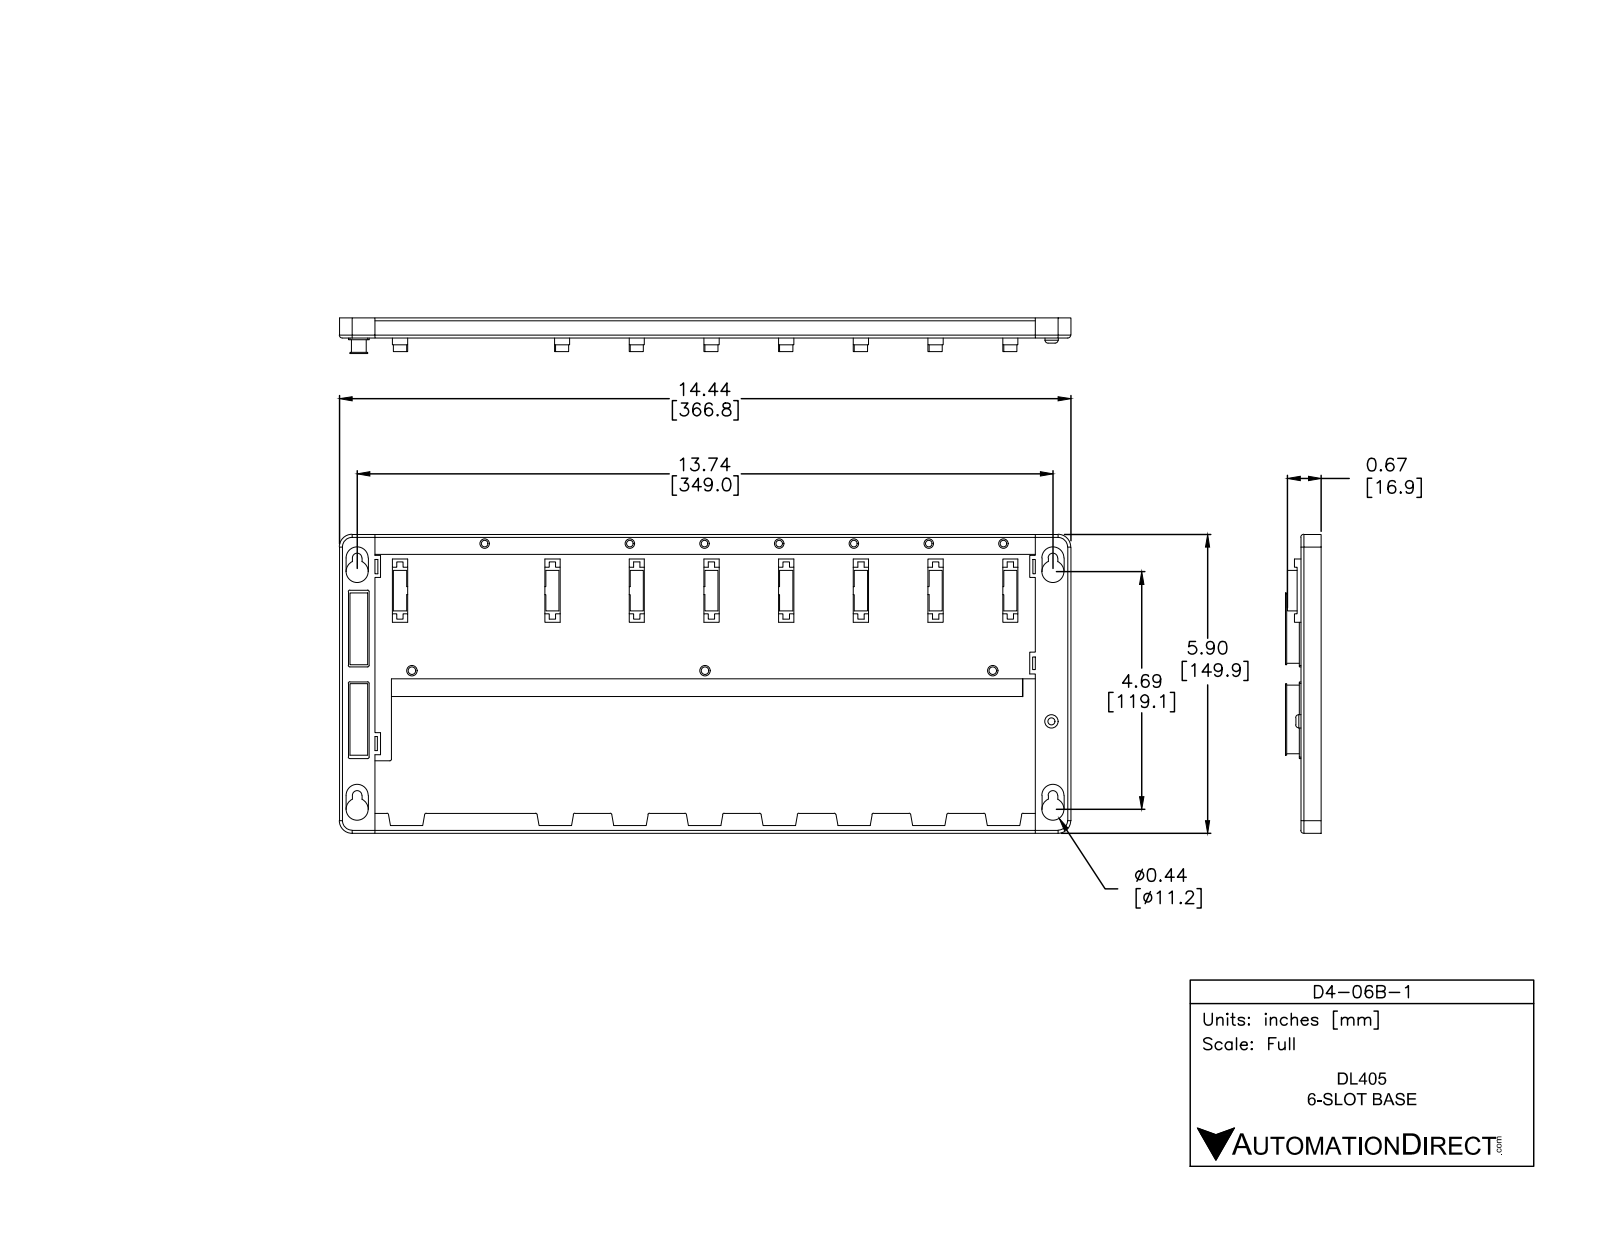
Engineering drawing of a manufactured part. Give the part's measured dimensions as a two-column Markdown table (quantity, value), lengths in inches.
| quantity | value |
| --- | --- |
| part name | D4-06B-1 |
| STEP written by | SolidWorks 2014 (AUTOMOTIVE_DESIGN) |
| units | inches |
| bodies | 1 solid, 517 faces (407 planar, 84 cylindrical, 26 other) |
| overall size | 14.44 × 5.9 × 0.706 |
| volume | 11.8 in³ |
| surface area | 307.2 in² |
| round holes (diameter × count) | 0.13 × 6, 0.44 × 4, 0.14 × 1 |
| round bosses / shafts (diameter × count) | 0.205 × 2, 0.26 × 1, 0.234 × 1, 0.205 × 1 |
| partial cylindrical surfaces (radius × count) | 0.03 × 26, 0.06 × 6, 0.095 × 4, 0.19 × 4, 0.22 × 4, 0.25 × 4 |
| main face-to-face distances | 0.05, 0.197, 0.147, 0.275, 0.225, 0.078, 0.35, 0.125, 0.3, 0.4 |
| hole center spacings | 2.95, 1.475, 1.475, 4.425, 4.69, 5.9, 13.74, 14.519 |
